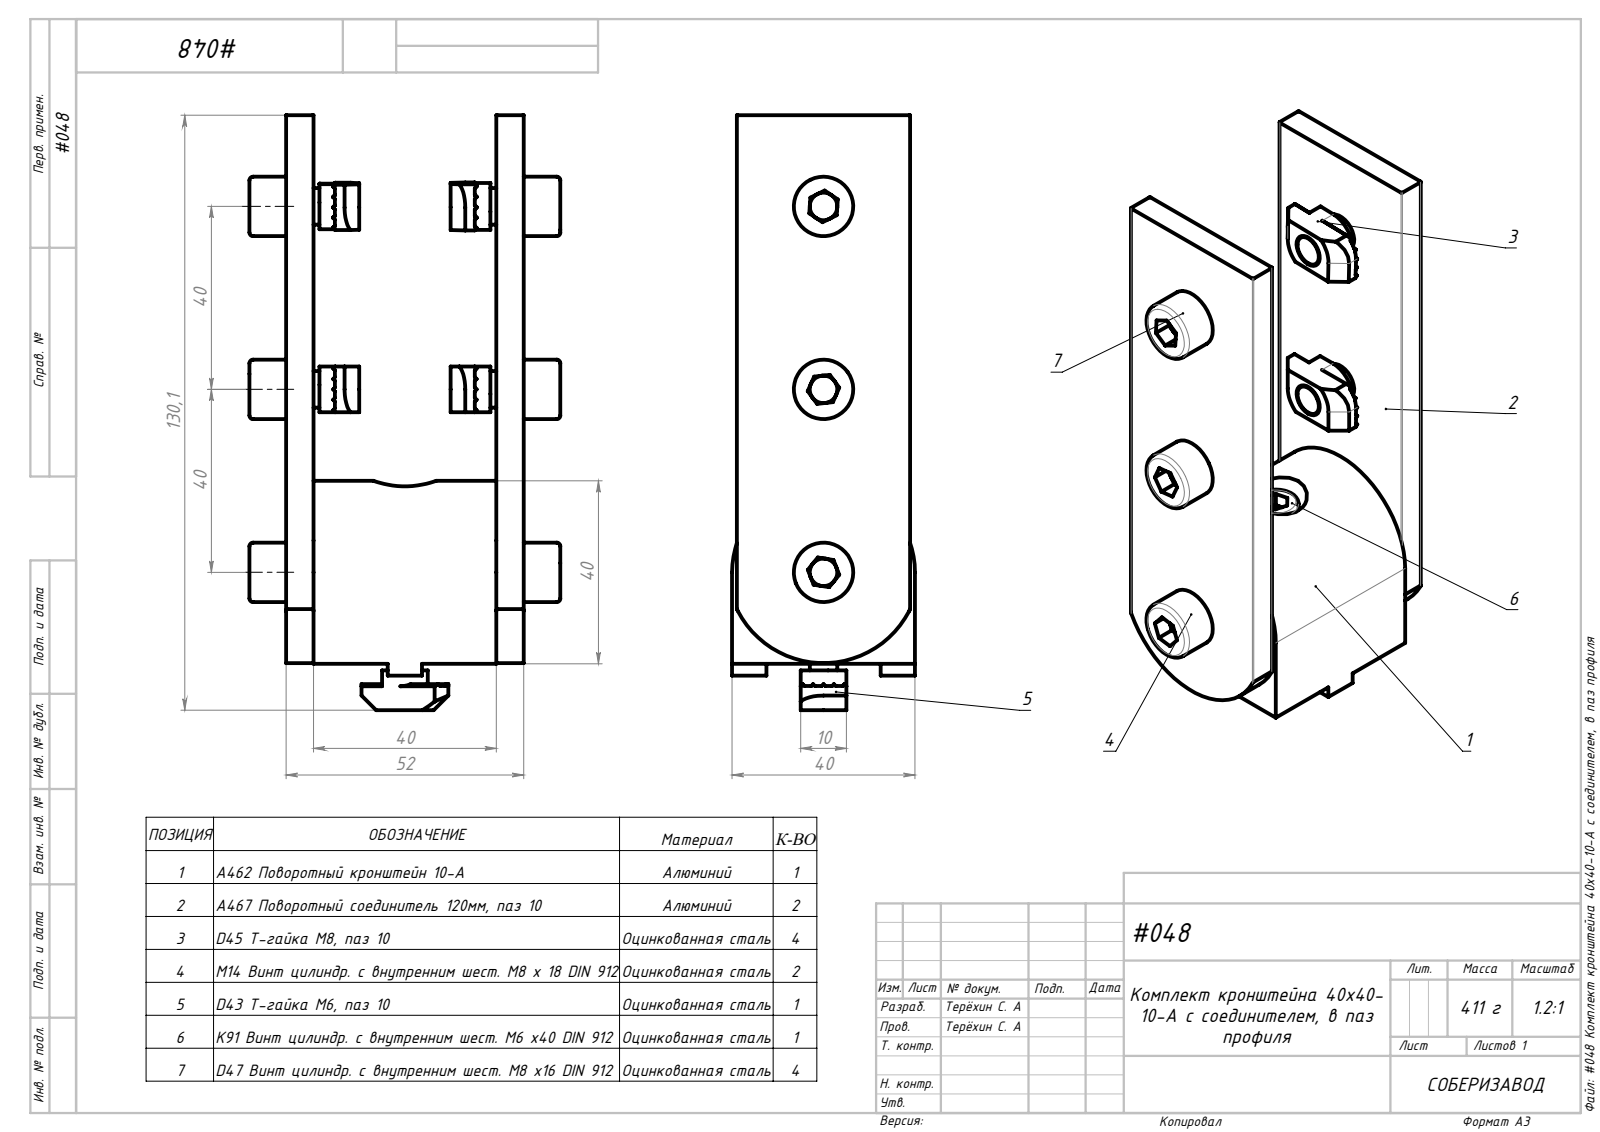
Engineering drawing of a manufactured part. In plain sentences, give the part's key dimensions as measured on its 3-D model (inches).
The part is named "D45 Т-гайка М8, паз 10_00; D47 Винт цилиндр. с внутренним шест. М8 х16 DIN 912; A467 Поворотный соединитель 120мм, паз 10; K91 Винт цилиндр. с внутренним шест. М6 х40 DIN 912 (+4 more)". Its 3-D file was written by "SolidWorks 2021 (AUTOMOTIVE_DESIGN)". It is 15 solids with 510 faces: 319 planar, 89 cylindrical and 102 other. Overall it measures 5.122 by 2.677 by 1.575 inches. Its volume is 7.374 cubic inches and its surface area 67.35 square inches. Round holes: 4 of diameter 0.335, 2 of diameter 0.264, 1 of diameter 0.197, 1 of diameter 0.256, 1 of diameter 0.5. Round bosses or shafts: 3 of diameter 0.512, 3 of diameter 0.315, 1 of diameter 0.394, 1 of diameter 0.236. Partial cylindrical surfaces (rounded edges, fillets, slot ends): 10 of radius 0.236, 8 of radius 0.008, 6 of radius 0.223, 1 of radius 0.787, 1 of radius 0.831. The main face-to-face distances are 0.236, 1.811, 1.575, 2.047, 0.041, 1.533, 1.492, 0.394, 0.63, 4.722. The hole center spacings are 1.575, 3.15.
